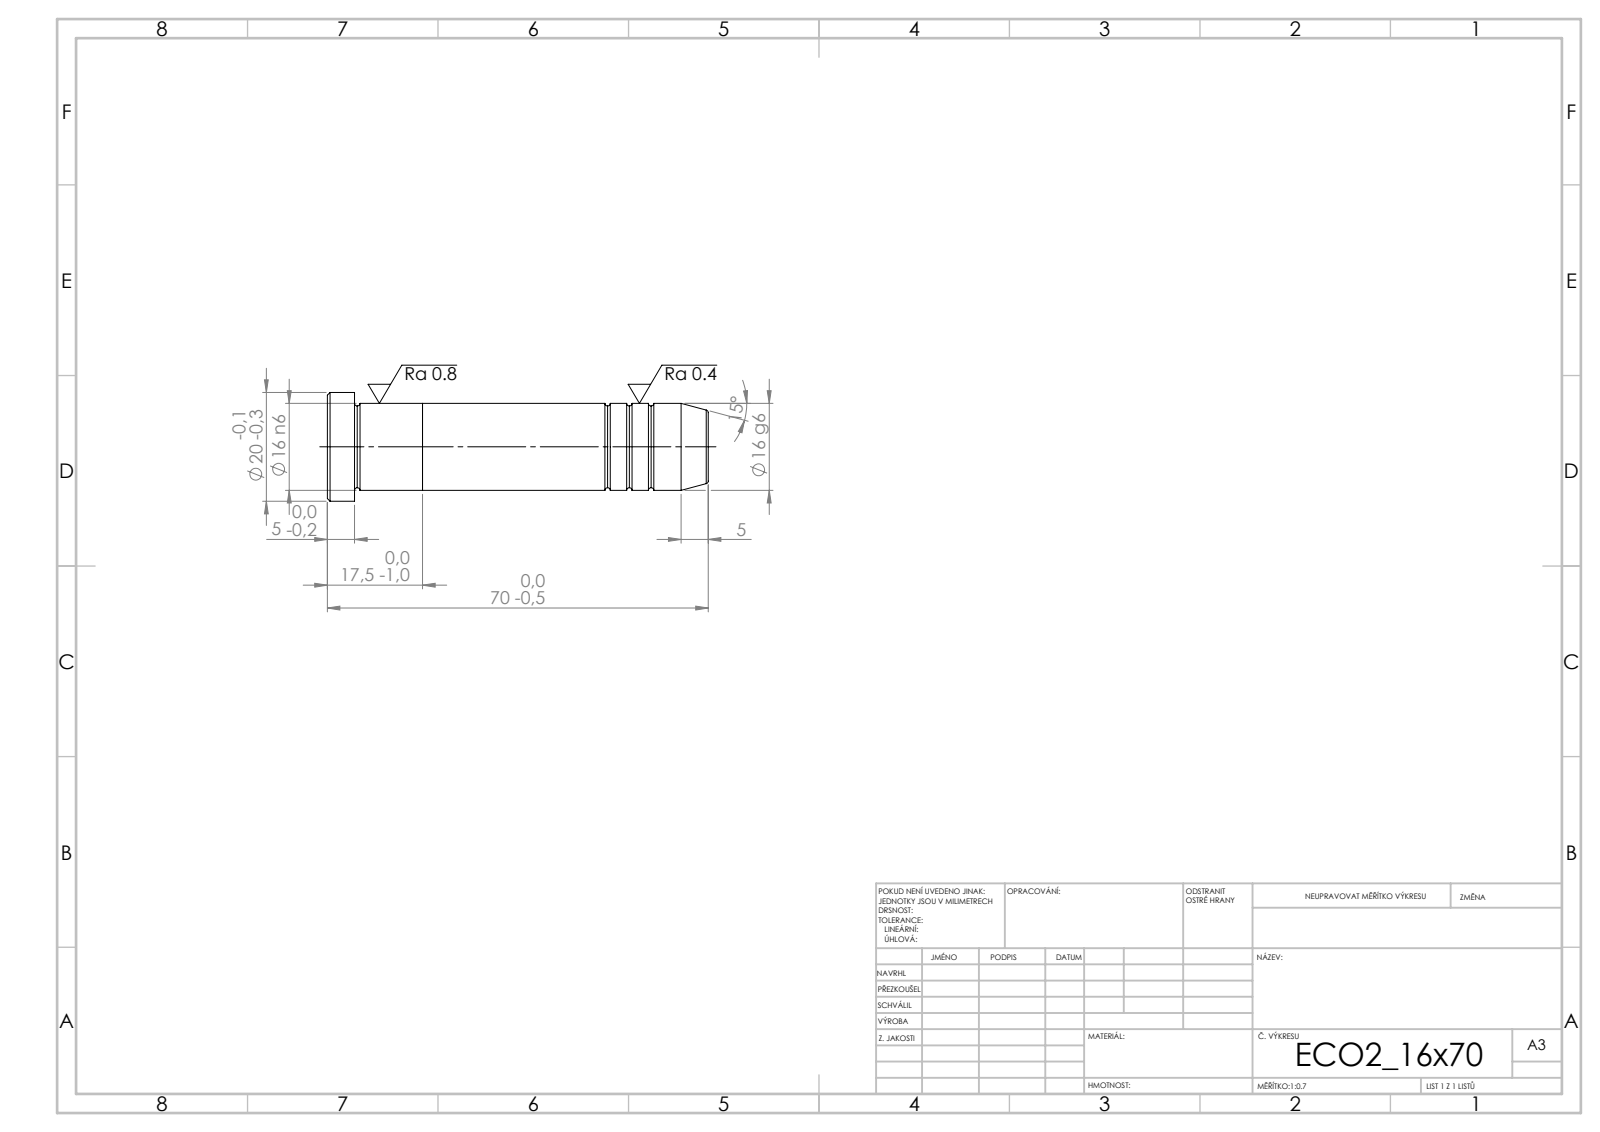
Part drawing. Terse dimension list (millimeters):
written by: SolidWorks 2019 (CONFIG_CONTROL_DESIGN)
unit: mm
bodies: 2 solids, 39 faces (5 planar, 12 cylindrical, 22 other)
size: 70 × 20 × 20
volume: 14 395 mm³; area: 4 616 mm²
bosses: 1× ⌀20, 1× ⌀16
face distances: 17.5, 52.5, 70, 65, 12.5, 5
